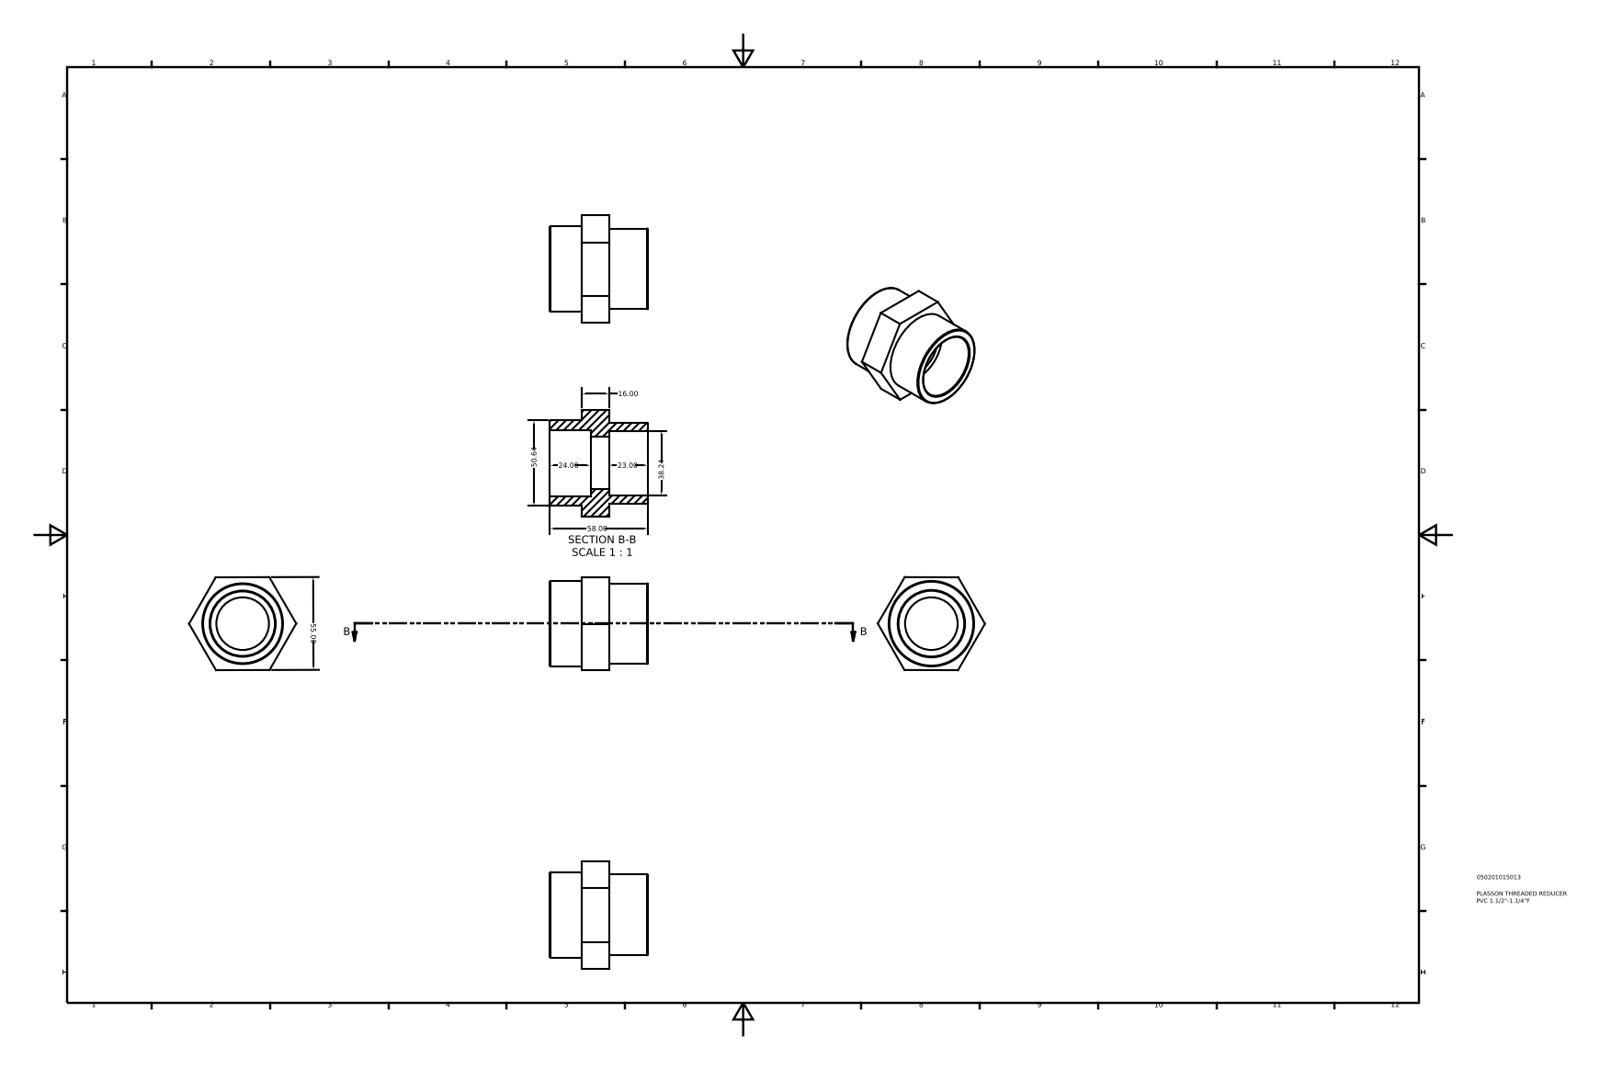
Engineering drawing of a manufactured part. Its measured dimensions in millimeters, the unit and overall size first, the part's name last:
Units: millimetres
Overall size (bounding box): 63.51 × 58 × 55.09
Round holes (diameter × count): ⌀31.16 ×1, ⌀38.24 ×1, ⌀38.95 ×1
Round bosses / shafts (diameter × count): ⌀50.64 ×1, ⌀47.8 ×1
Main face-to-face distances: 55.04, 35, 19, 16, 58, 39, 23, 55, 24, 5
Volume: 58 024 mm³ · Surface area: 19 903 mm²
Bodies: 1 solid, 21 faces (12 planar, 5 cylindrical, 4 other)
Part name (STEP PRODUCT): 050201015013
STEP written by: Autodesk Inventor 2015 (AUTOMOTIVE_DESIGN)
